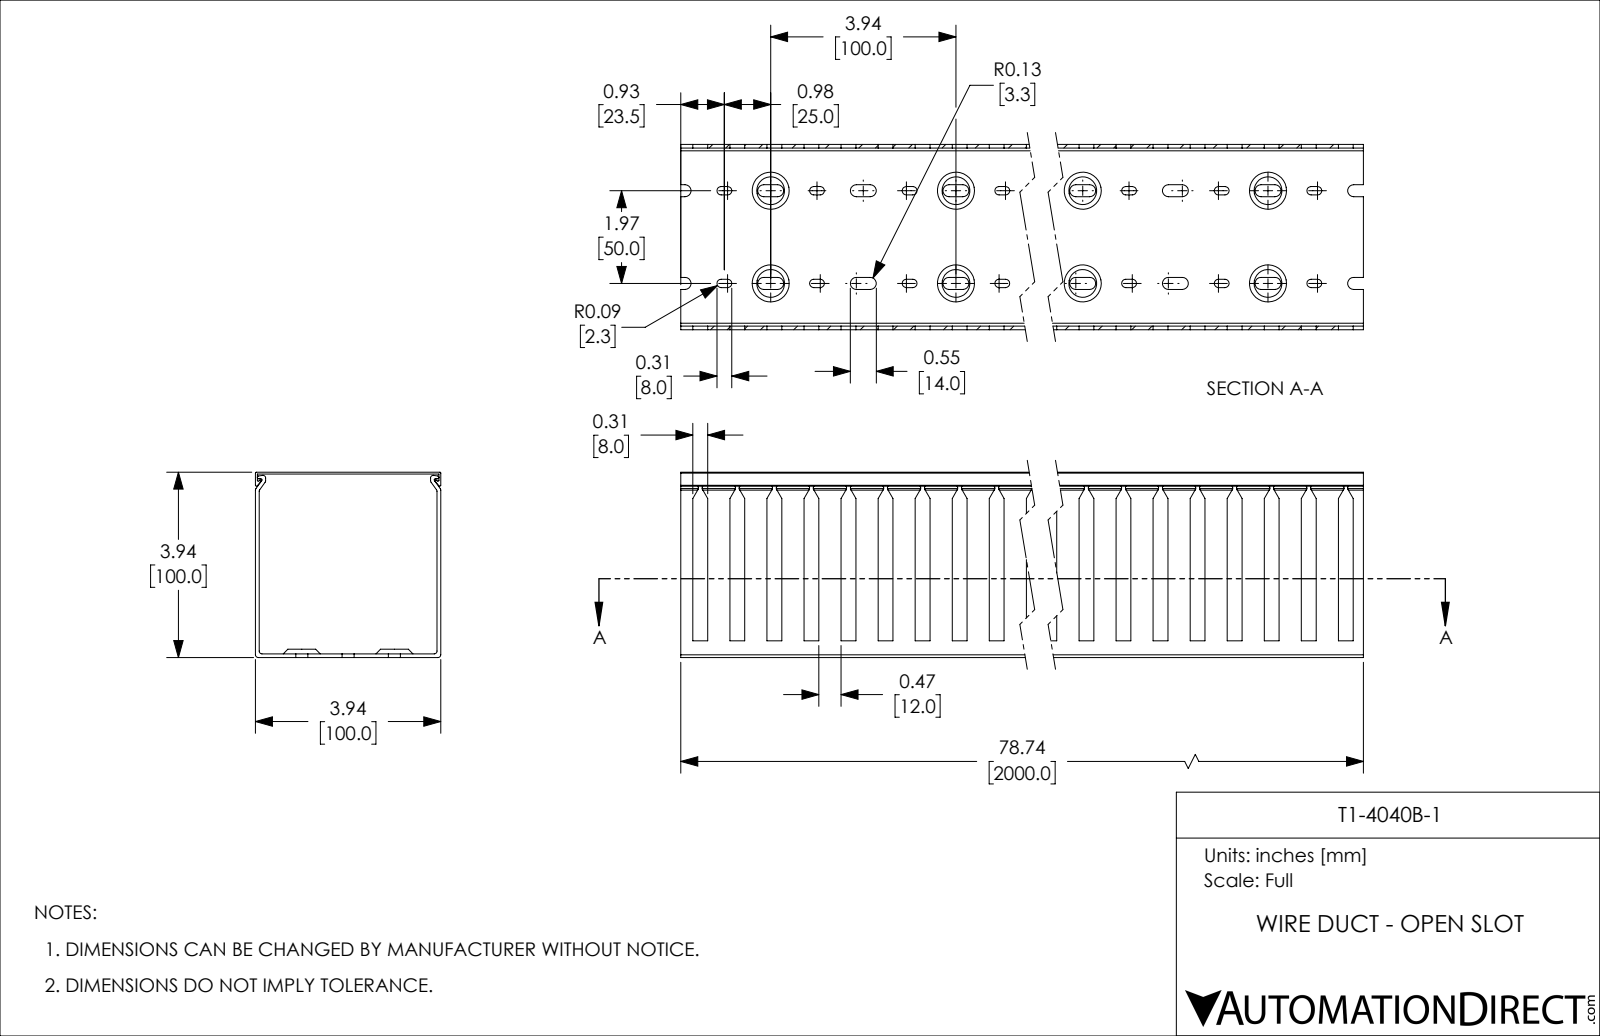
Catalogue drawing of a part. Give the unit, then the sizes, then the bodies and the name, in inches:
Units: inches
Overall size (bounding box): 78.74 × 3.937 × 3.937
Partial cylindrical surfaces — rounded edges, fillets, slot ends (radius × count): R0.128 ×200, R0.089 ×160, R0.059 ×12, R0.02 ×8, R0.03 ×6
Main face-to-face distances: 0.079, 3.858, 3.937, 0.039, 3.898, 3.819, 3.78, 0.177, 3.72, 0.217
Volume: 85.31 in³ · Surface area: 2 540 in²
Bodies: 2 solids, 1573 faces (762 planar, 731 cylindrical, 80 other)
Part name (STEP PRODUCT): T1-4040B-1
STEP written by: SolidWorks 2021 (CONFIG_CONTROL_DESIGN)
